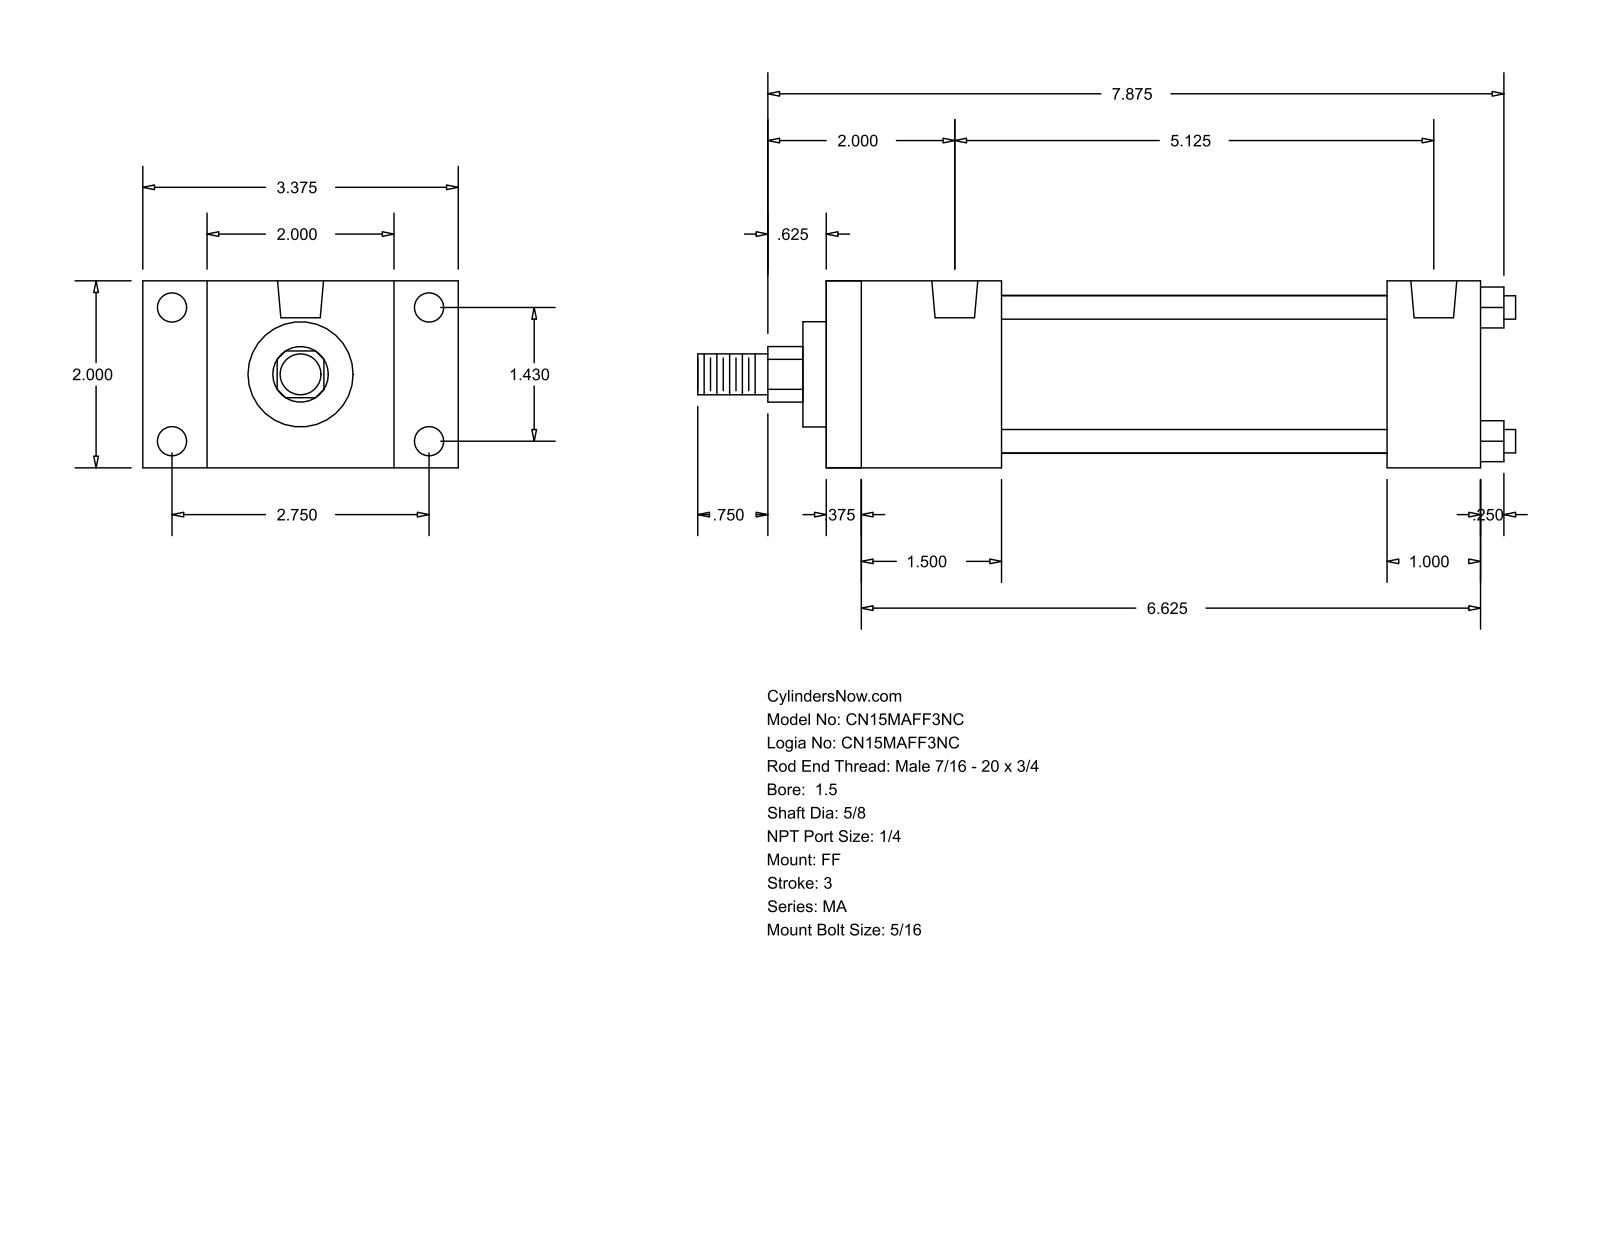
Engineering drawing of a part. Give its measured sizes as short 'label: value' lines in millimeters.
name: MA_FF__0150_0.625
written by: GSSL Pune (CONFIG_CONTROL_DESIGN)
unit: mm
bodies: 0 solids, 92 faces (64 planar, 28 cylindrical, 0 other)
size: 222.25 × 85.72 × 50.8
holes: 8× ⌀7.94, 2× ⌀12.49
bosses: 4× ⌀6.35, 1× ⌀42.93, 1× ⌀28.57, 1× ⌀15.88, 1× ⌀11.11
rounds: 1× R7.54
face distances: 50.8, 177.8, 9.52, 168.28, 25.4, 47.62, 152.4, 38.1, 142.88, 104.78
hole spacings: 36.32, 69.84, 78.72, 130.17
